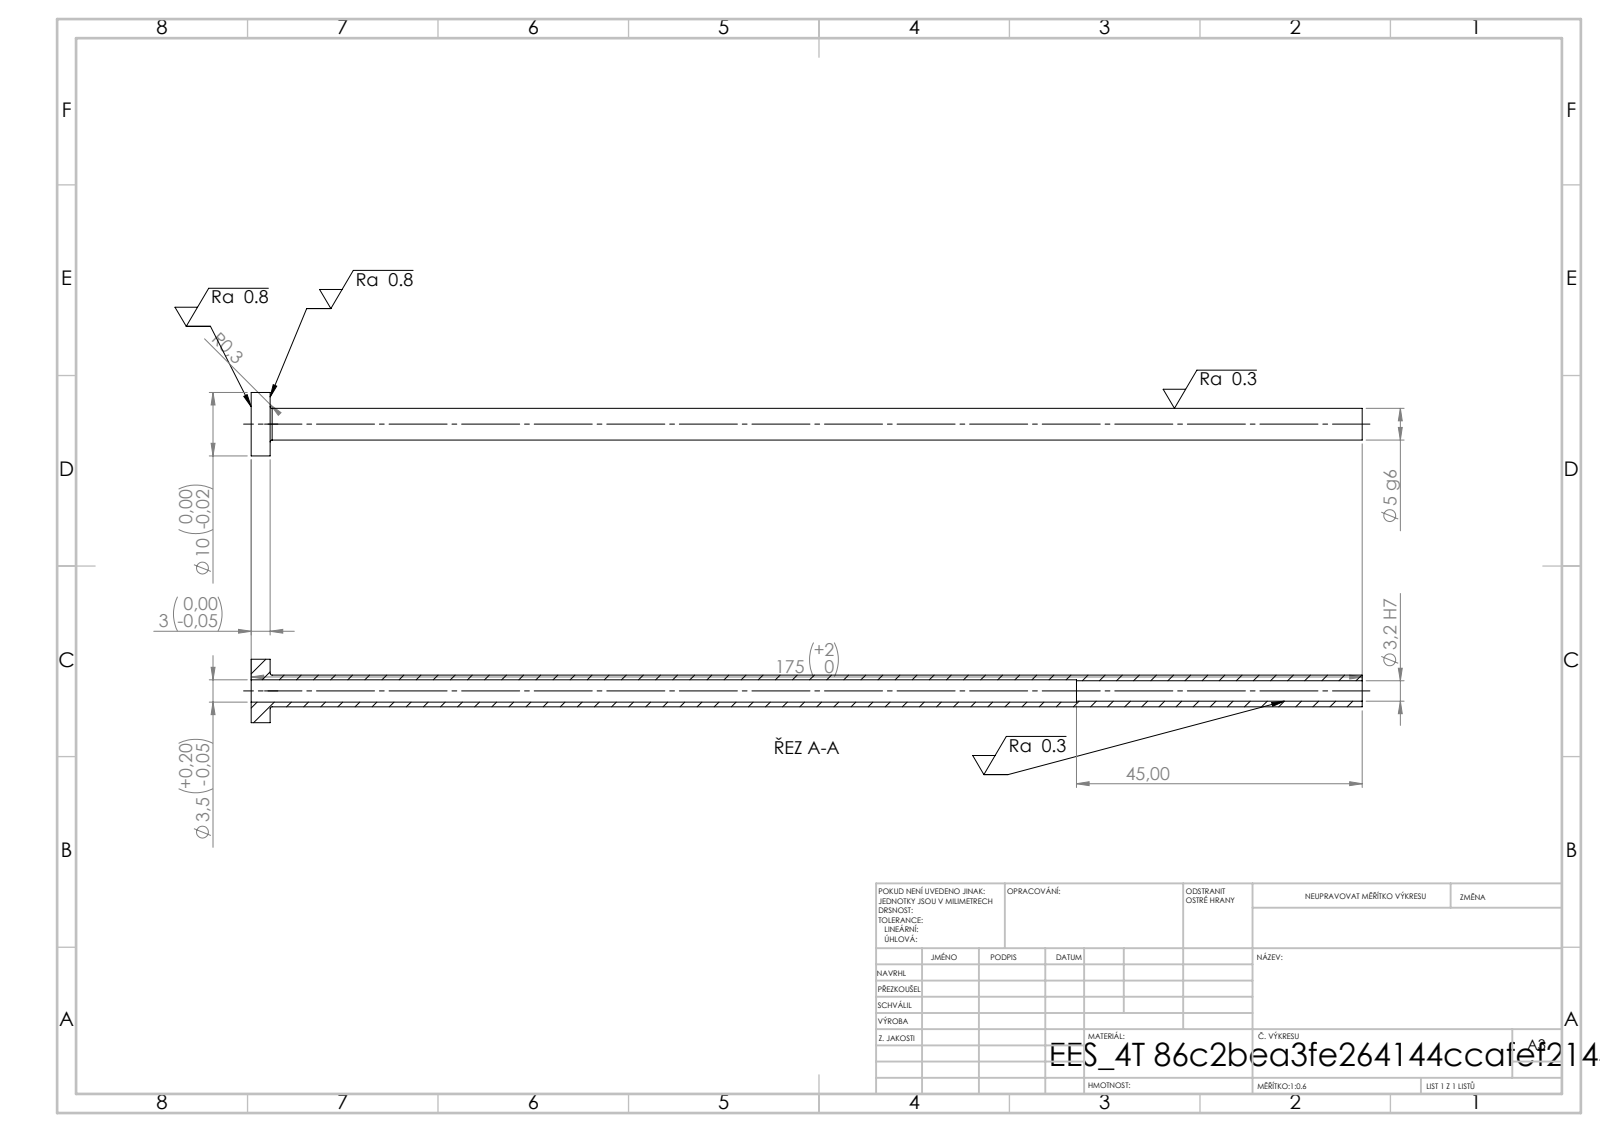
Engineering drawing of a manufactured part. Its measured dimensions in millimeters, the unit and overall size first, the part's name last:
Units: millimetres
Overall size (bounding box): 175 × 10 × 10
Round holes (diameter × count): ⌀3.2 ×1, ⌀3.5 ×1
Round bosses / shafts (diameter × count): ⌀10 ×1, ⌀5 ×1
Main face-to-face distances: 3, 175, 172, 130, 127, 45
Volume: 2 000 mm³ · Surface area: 4 817 mm²
Bodies: 1 solid, 14 faces (4 planar, 8 cylindrical, 2 other)
STEP written by: SolidWorks 2019 (CONFIG_CONTROL_DESIGN)
